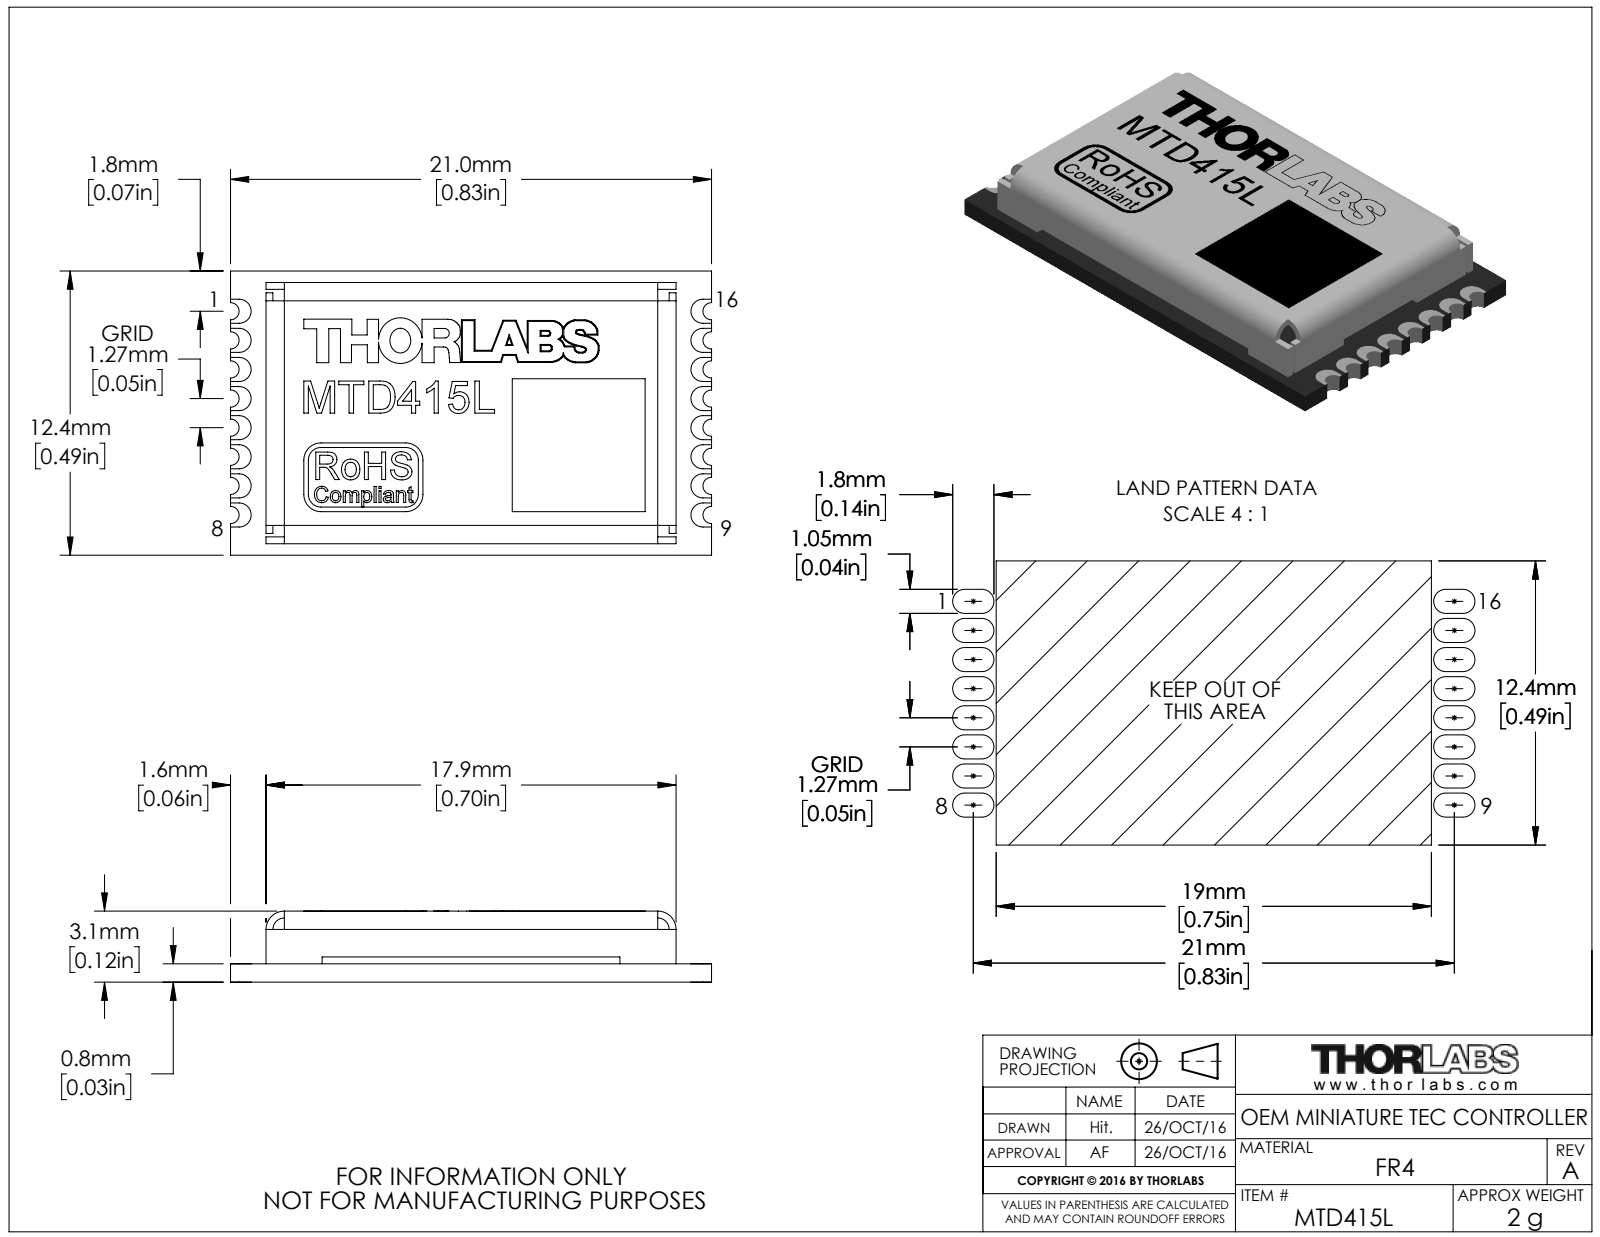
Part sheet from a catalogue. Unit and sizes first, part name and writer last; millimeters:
Units: millimetres
Overall size (bounding box): 21 × 12.4 × 3.1
Partial cylindrical surfaces — rounded edges, fillets, slot ends (radius × count): R0.38 ×16, R0.53 ×16, R0.5 ×4, R0.55 ×4, R0.75 ×4, R0.8 ×4
Main face-to-face distances: 0.8, 2, 2.3, 2.8, 3.1, 11.1, 0.5, 11.6, 11.9, 17.6
Volume: 292 mm³ · Surface area: 1 174 mm²
Bodies: 2 solids, 933 faces (726 planar, 88 cylindrical, 119 other)
Part name (STEP PRODUCT): MTN007705-E0W
STEP written by: SolidWorks 2016 (AUTOMOTIVE_DESIGN)
